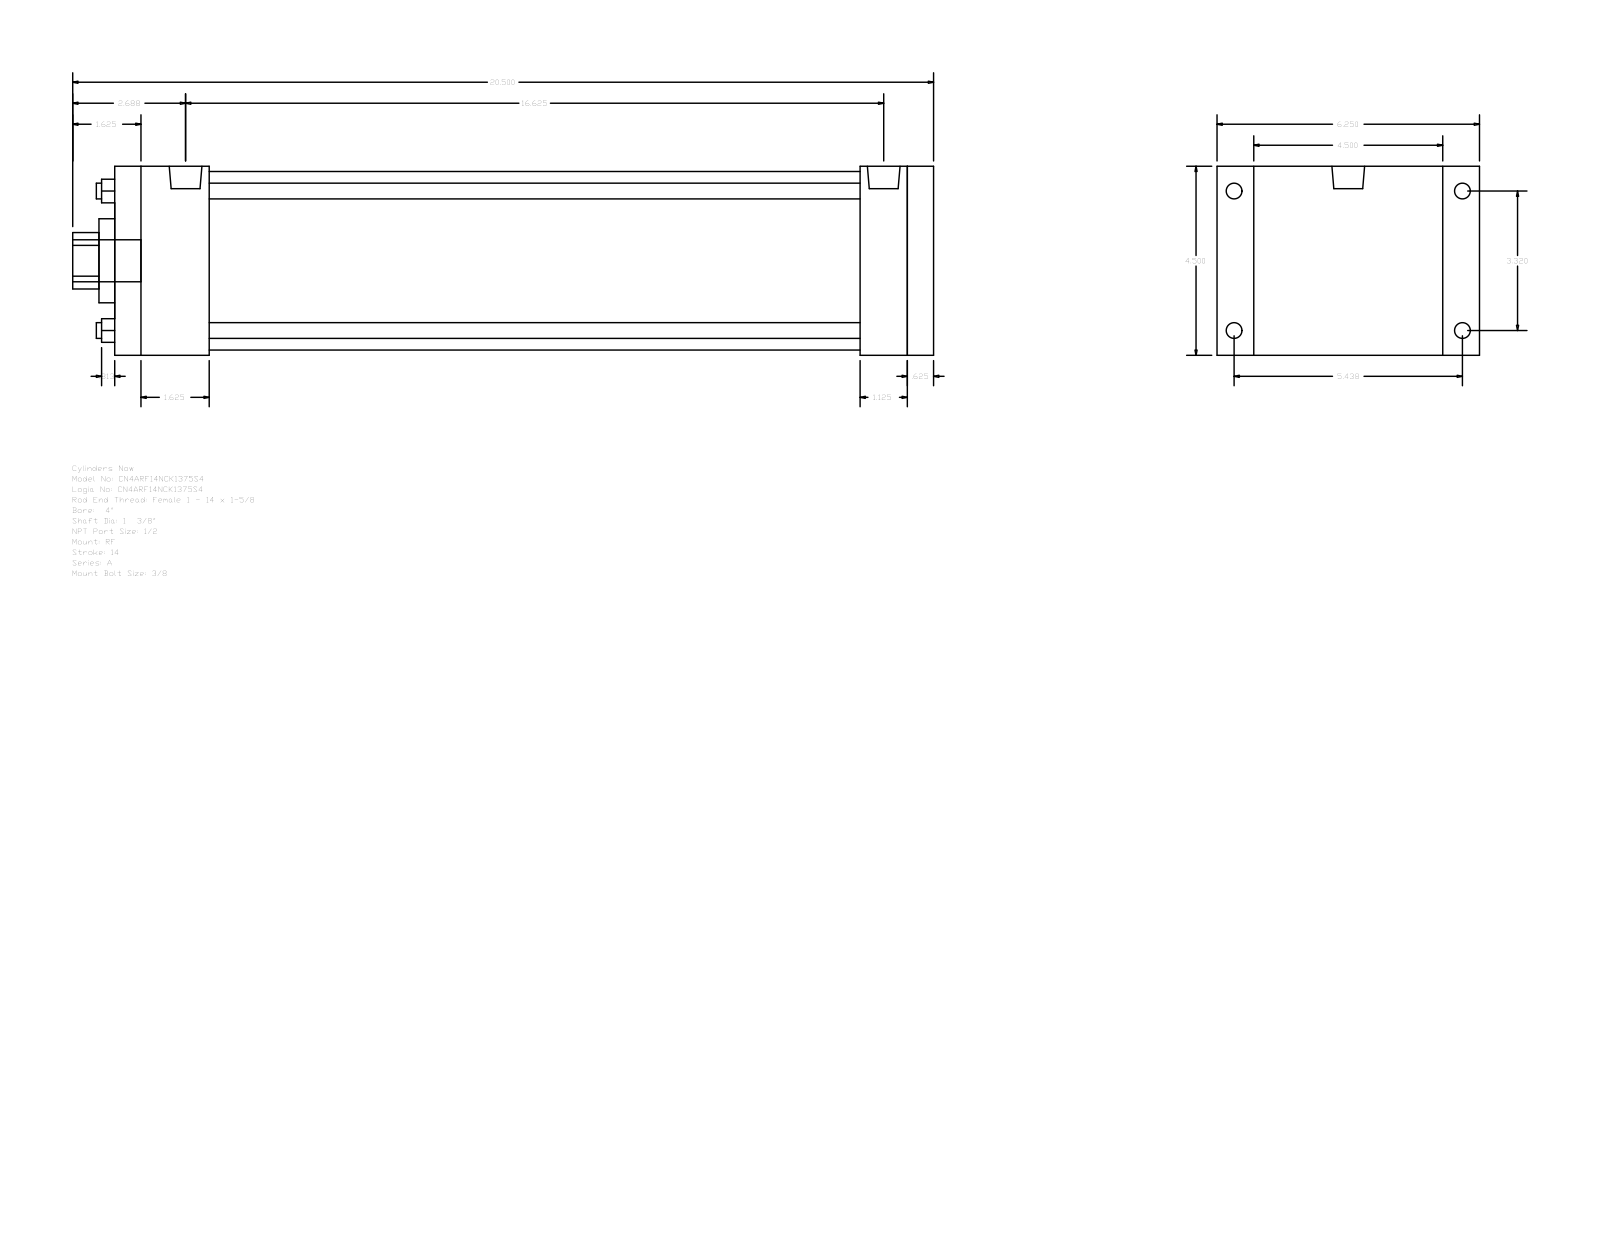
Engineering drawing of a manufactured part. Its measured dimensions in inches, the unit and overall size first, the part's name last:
Units: inches
Overall size (bounding box): 20.5 × 6.25 × 4.5
Round holes (diameter × count): ⌀0.375 ×4, ⌀1.375 ×1, ⌀2 ×1, ⌀4.25 ×1
Round bosses / shafts (diameter × count): ⌀0.375 ×4, ⌀0.344 ×4, ⌀0.778 ×2, ⌀1 ×1
Partial cylindrical surfaces — rounded edges, fillets, slot ends (radius × count): R0.672 ×1
Main face-to-face distances: 4.5, 19.5, 0.625, 18.875, 1.125, 0.875, 5.375, 17.75, 1.75, 2.25
Hole centre spacings: 2.347, 3.32, 4.695
Bodies: 0 solids, 92 faces (64 planar, 28 cylindrical, 0 other)
Part name (STEP PRODUCT): A_RF__0400_1.375
STEP written by: GSSL Pune (CONFIG_CONTROL_DESIGN)
